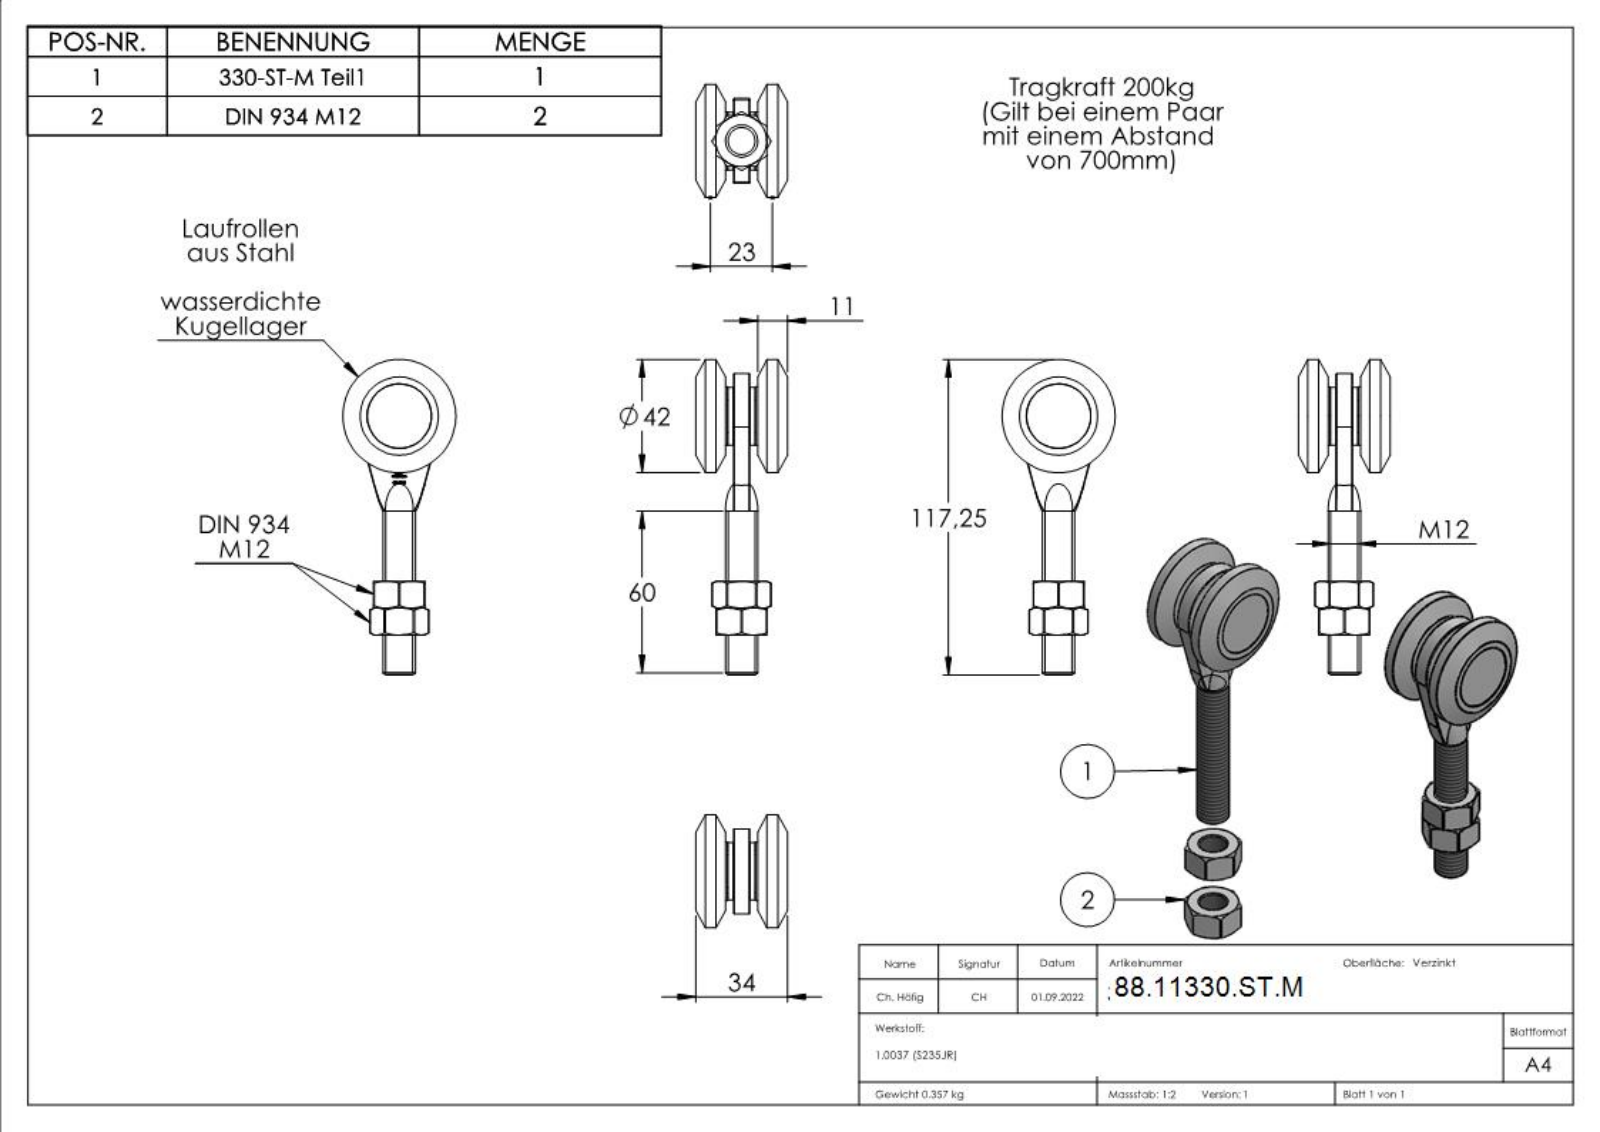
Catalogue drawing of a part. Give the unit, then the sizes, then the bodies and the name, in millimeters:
Units: millimetres
Overall size (bounding box): 117.25 × 42 × 34
Round holes (diameter × count): ⌀10.2 ×1, ⌀12.2 ×1, ⌀24 ×1
Round bosses / shafts (diameter × count): ⌀42 ×1, ⌀23.8 ×1, ⌀21.7 ×1, ⌀21.5 ×1, ⌀12.1 ×1, ⌀12 ×1
Partial cylindrical surfaces — rounded edges, fillets, slot ends (radius × count): R0.5 ×12, R0.2 ×4, R15.75 ×1
Main face-to-face distances: 19, 0.8, 13, 19.1, 10.8, 22, 10.9, 21.2, 8.2, 22.1
Volume: 45 792 mm³ · Surface area: 19 764 mm²
Bodies: 7 solids, 370 faces (171 planar, 36 cylindrical, 163 other)
Part name (STEP PRODUCT): DIN 934 M4-M20_DIN 934 M12; 330-X-X Konfig_330-ST-M Teil1; 330-ST-M
STEP written by: SolidWorks 2018 (CONFIG_CONTROL_DESIGN)
